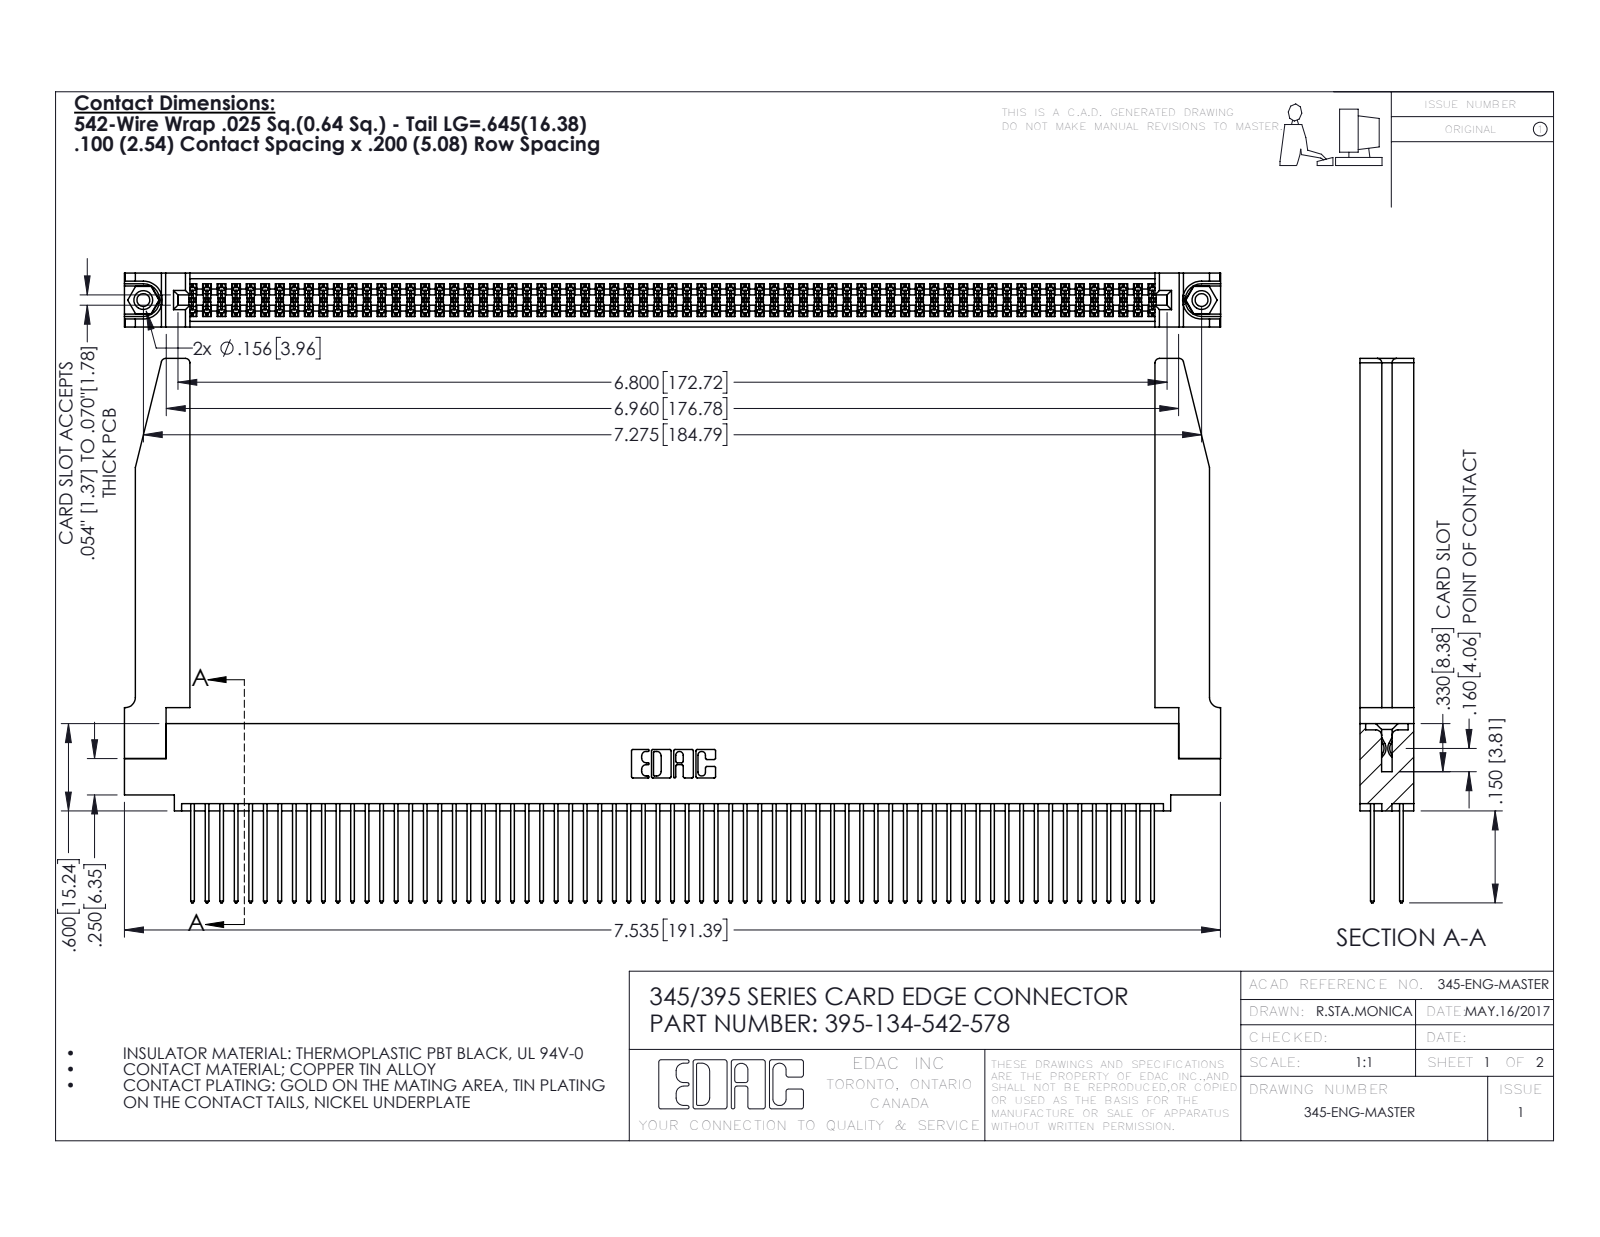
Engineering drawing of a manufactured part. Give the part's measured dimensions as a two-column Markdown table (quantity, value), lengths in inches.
| quantity | value |
| --- | --- |
| part name | 395-134-542-578; 345-220-078_345-220-078; 345-292-001_345-293-142; 345-250-001_345-250-001-102 (+1 more) |
| STEP written by | SolidWorks 2016 (CONFIG_CONTROL_DESIGN) |
| units | inches |
| bodies | 139 solids, 7064 faces (4648 planar, 2364 cylindrical, 52 other) |
| overall size | 7.536 × 3.742 × 0.37 |
| volume | 1.657 in³ |
| surface area | 60.42 in² |
| round holes (diameter × count) | 0.089 × 2, 0.125 × 2, 0.156 × 2, 0.064 × 1 |
| round bosses / shafts (diameter × count) | 0.155 × 2 |
| partial cylindrical surfaces (radius × count) | 0.006 × 201, 0.01 × 134, 0.01 × 22, 0.03 × 8, 0.007 × 6, 0.031 × 6, 0.026 × 3, 0.014 × 2 |
| main face-to-face distances | 0.072, 0.298, 0.37, 0.098, 0.272, 0.025, 0.2, 0.225, 0.175, 0.149 |
| hole center spacings | 0.27, 7.039, 7.275 |
